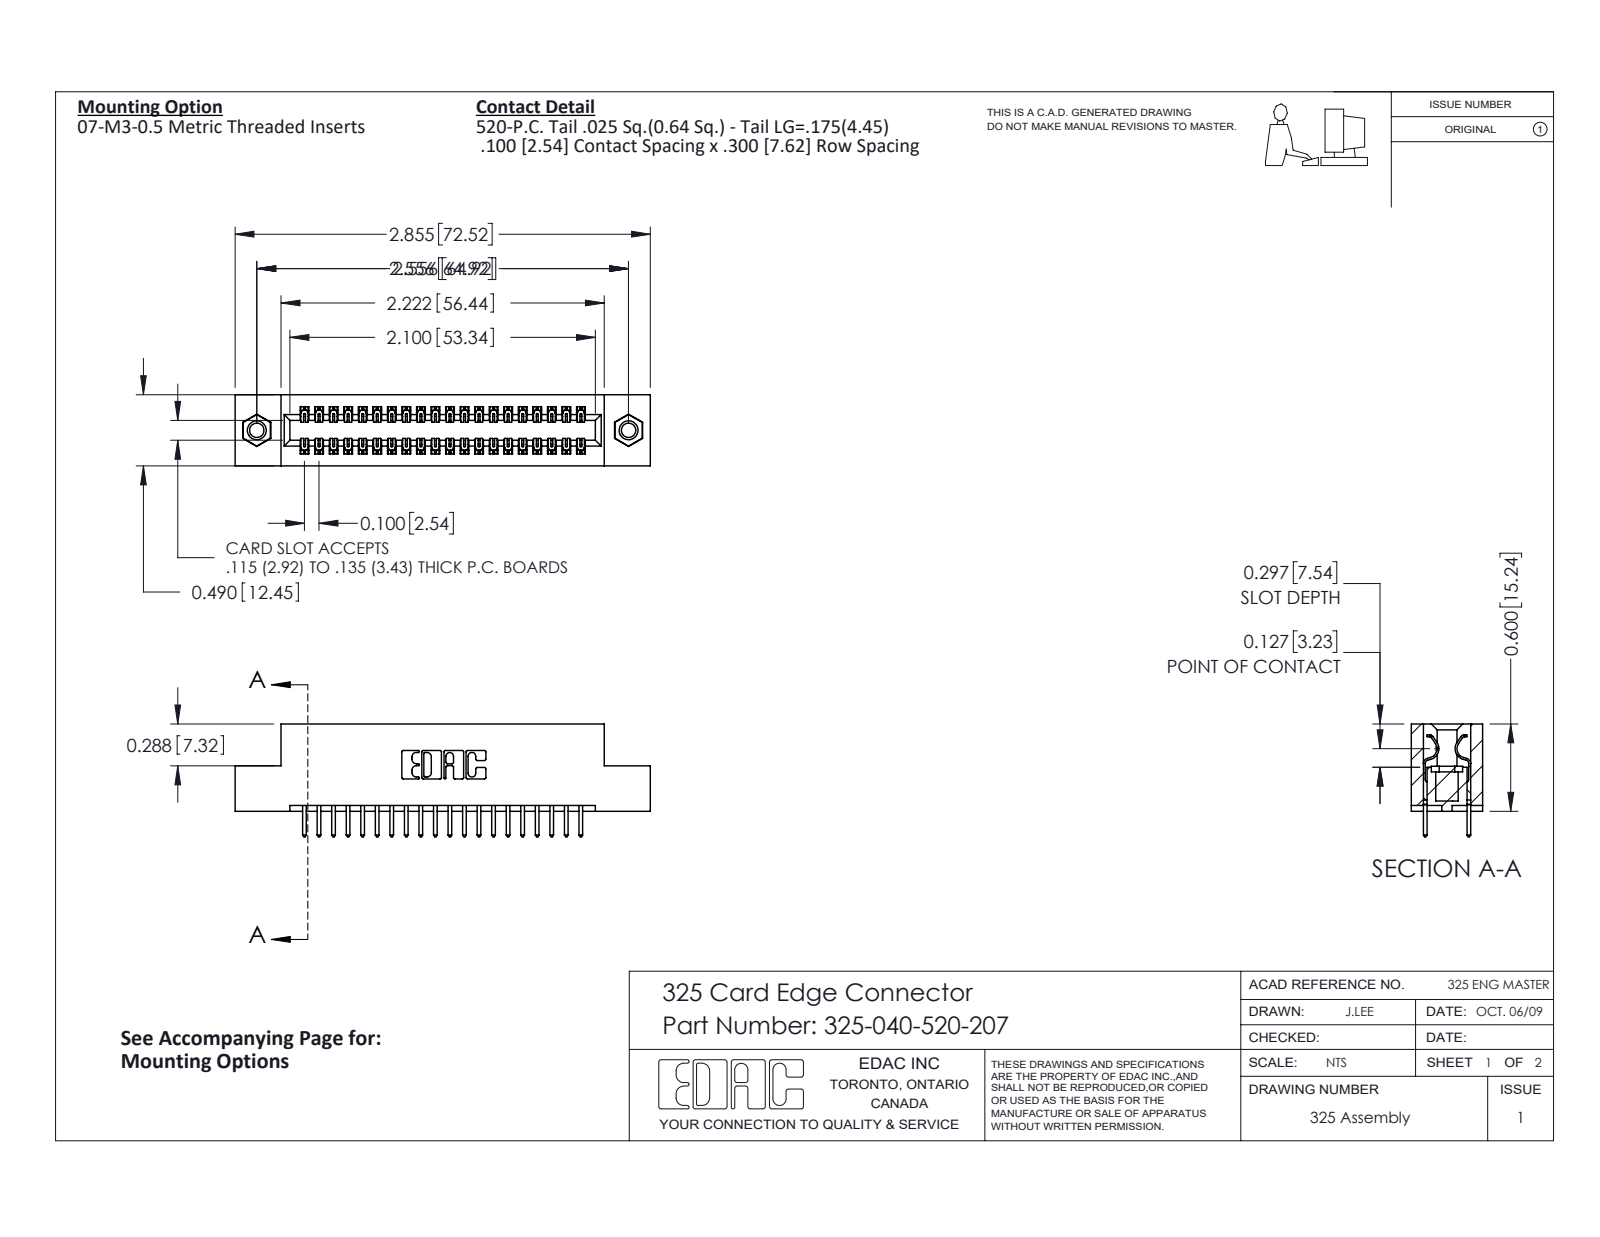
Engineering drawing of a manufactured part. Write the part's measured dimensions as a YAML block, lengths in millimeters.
part_name: "325-040-520-207; 325-292-001_325-293-120; 325 Part_TI; 345-250-001_345-250-005-103"
step_written_by: "SolidWorks 2016 (CONFIG_CONTROL_DESIGN)"
units: millimeters
bodies: {solids: 43, faces: 2254, planar: 1542, cylindrical: 696, other: 16}
overall_size: [72.5, 19.7, 12.4]
volume: 9140
surface_area: 10490
round_holes:
  - {diameter: 2.5, count: 2}
  - {diameter: 3.2, count: 2}
  - {diameter: 4.1, count: 2}
round_bosses_or_shafts:
  - {diameter: 3.9, count: 2}
partial_cylinders:
  - {radius: 0.2, count: 60}
  - {radius: 0.3, count: 40}
  - {radius: 0.3, count: 22}
  - {radius: 0.2, count: 6}
  - {radius: 0.8, count: 6}
  - {radius: 0.7, count: 3}
  - {radius: 0.4, count: 2}
  - {radius: 0.6, count: 2}
face_to_face_distances: [2.1, 10.3, 7.6, 12.4, 2.7, 9.7, 0.6, 8.3, 1, 2.5]
hole_center_spacings: [64.9]
